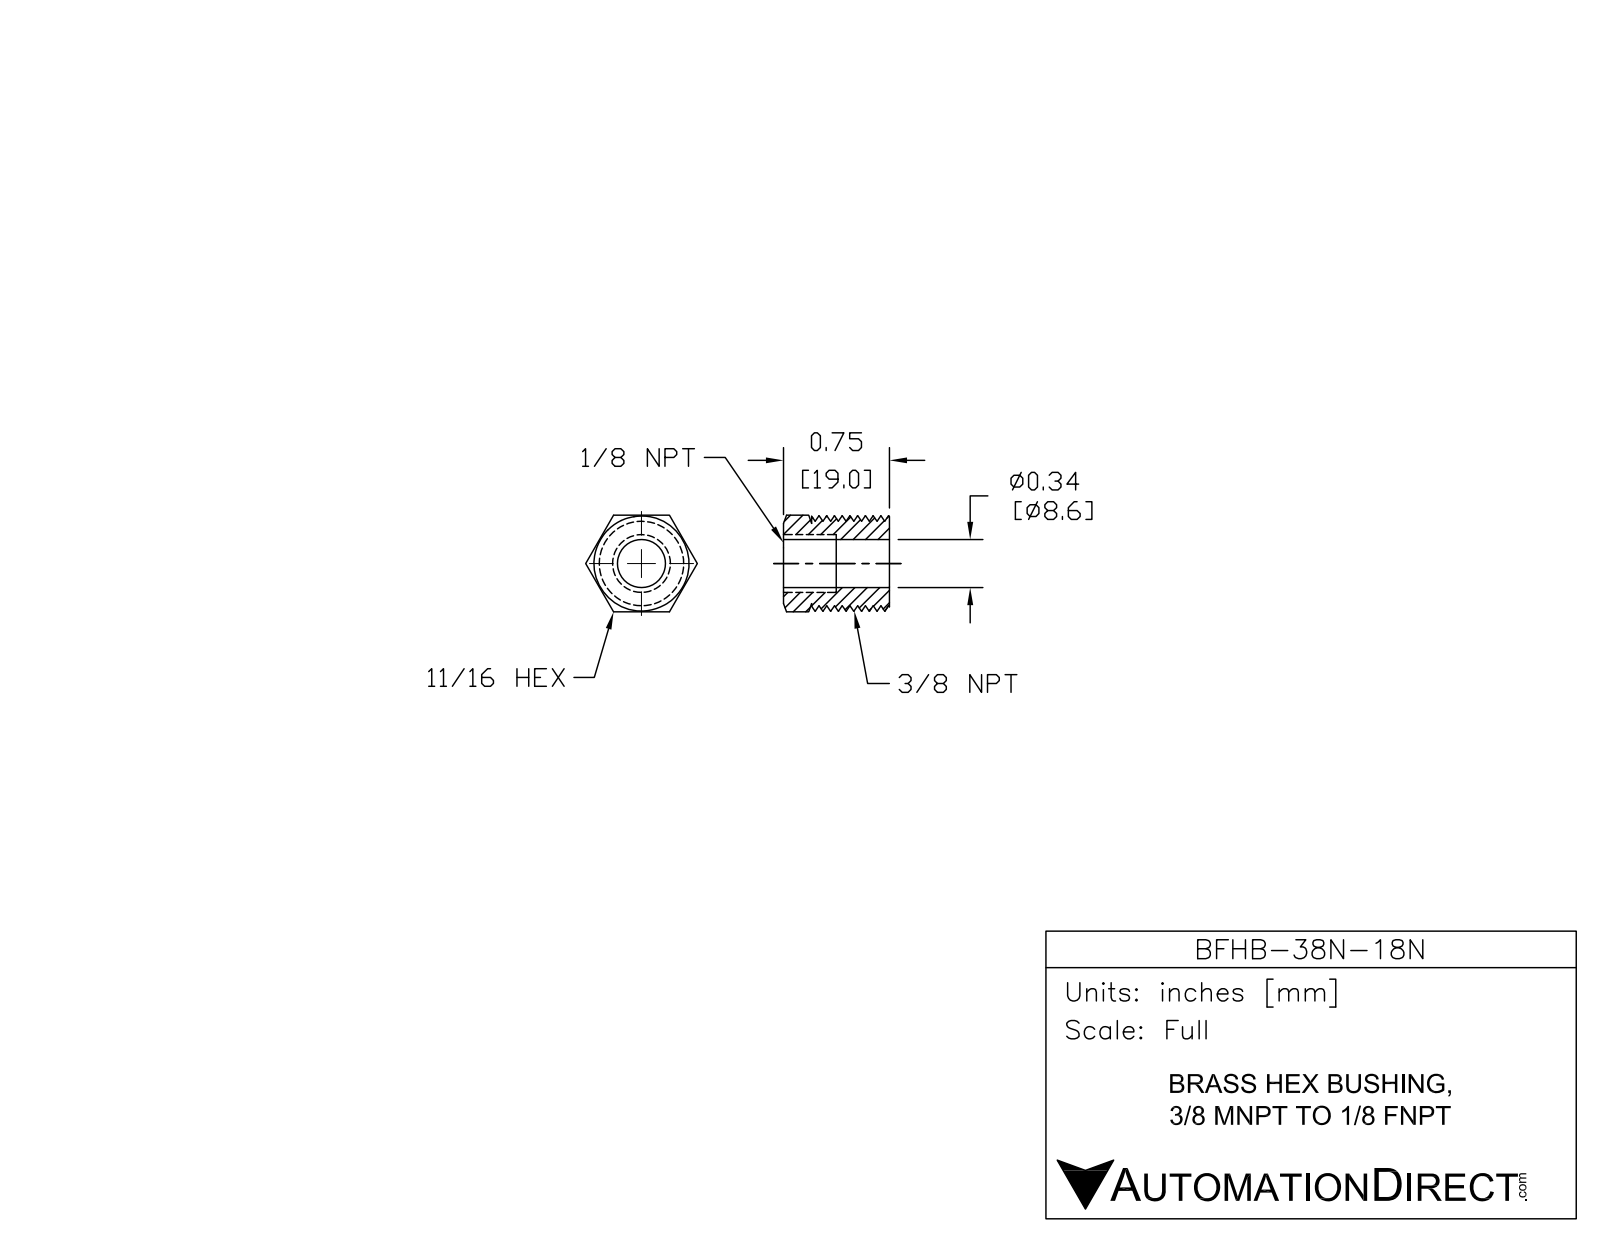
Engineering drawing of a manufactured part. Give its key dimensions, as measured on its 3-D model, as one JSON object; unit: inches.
{"part_name": "BFHB-38N-18N", "step_written_by": "SolidWorks 2015 (CONFIG_CONTROL_DESIGN)", "units": "inches", "bodies": {"solids": 1, "faces": 39, "planar": 10, "cylindrical": 23, "other": 6}, "overall_size": [0.794, 0.753, 0.688], "volume_in3": 0.187, "surface_area_in2": 3.841, "round_holes": [[0.34, 1]], "round_bosses_or_shafts": [[0.675, 1]], "face_to_face_distances": [0.687, 0.752, 0.2, 0.552]}
